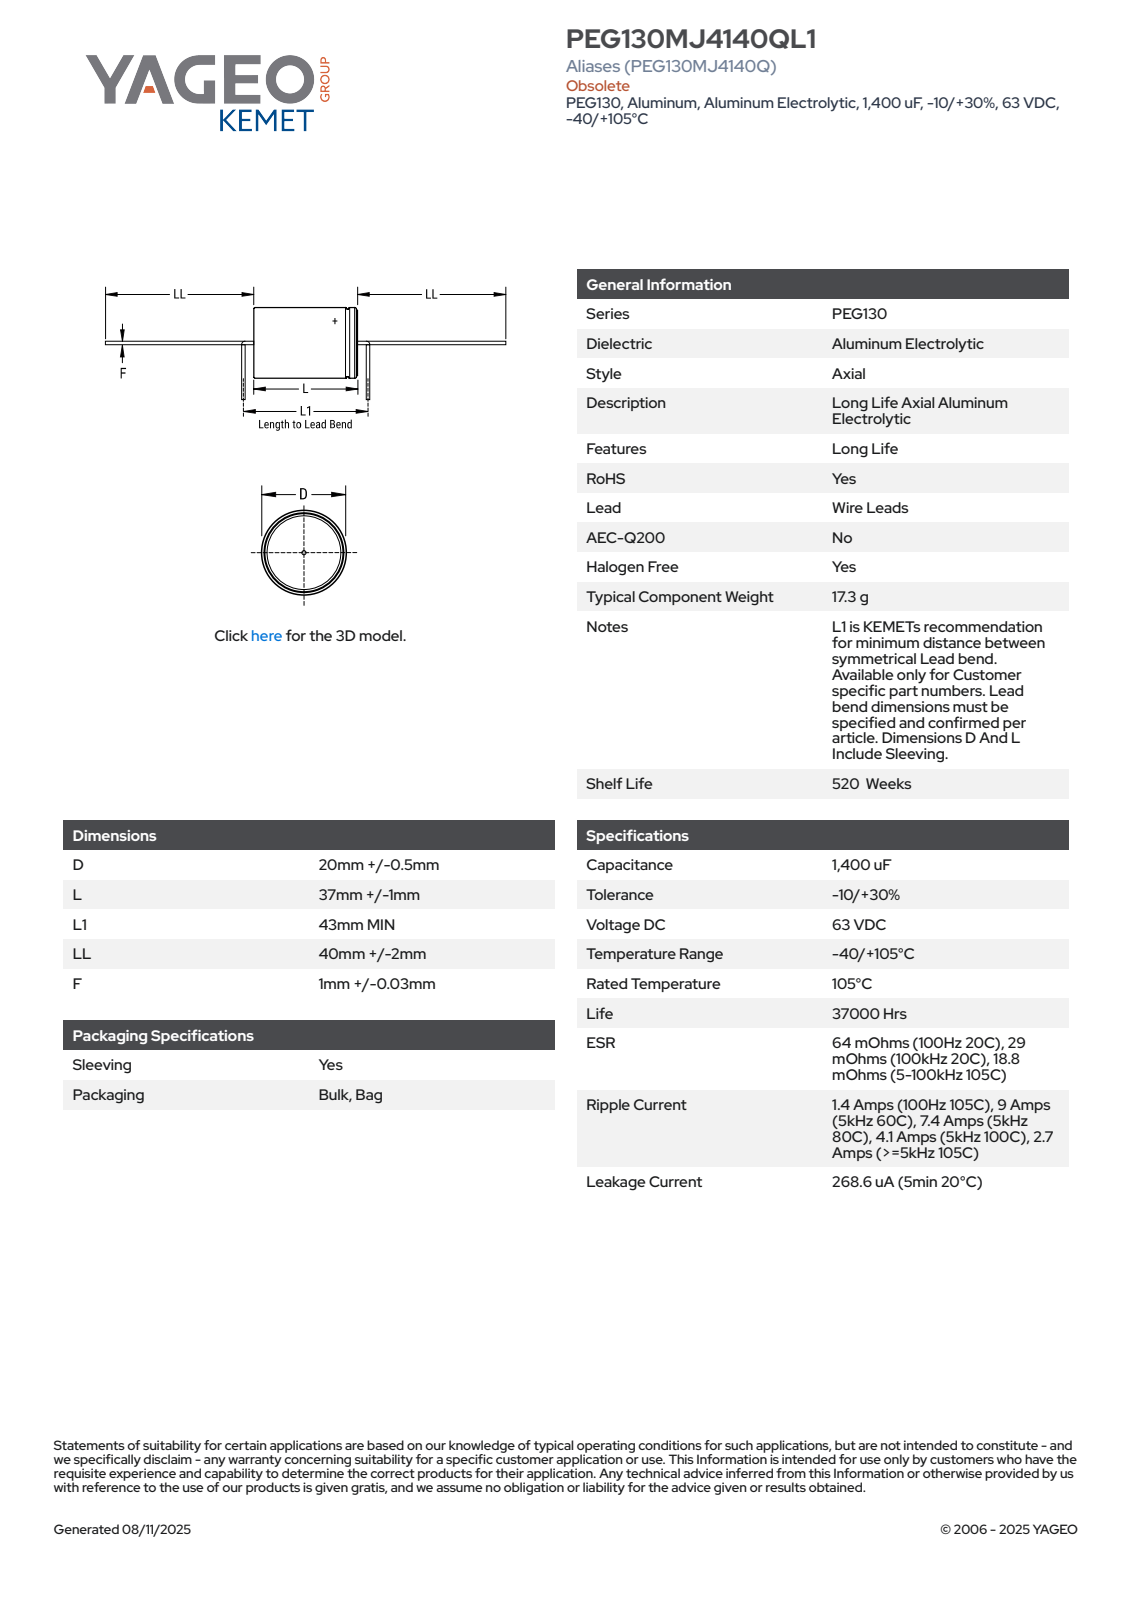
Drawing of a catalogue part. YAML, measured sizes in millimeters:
part_name: "CAA_PEG124_20X37_D20.5L38LL42F1.03"
step_written_by: "SolidWorks 2014 (AUTOMOTIVE_DESIGN)"
units: millimeters
bodies: {solids: 1, faces: 99, planar: 27, cylindrical: 29, other: 43}
overall_size: [122, 20.5, 20.5]
volume: 12305
surface_area: 3448
round_holes:
  - {diameter: 19.5, count: 1}
round_bosses_or_shafts:
  - {diameter: 20.5, count: 1}
  - {diameter: 20, count: 1}
  - {diameter: 1.03, count: 1}
partial_cylinders:
  - {radius: 10.24, count: 1}
face_to_face_distances: [37, 38, 1, 42, 80, 79, 122, 43]
